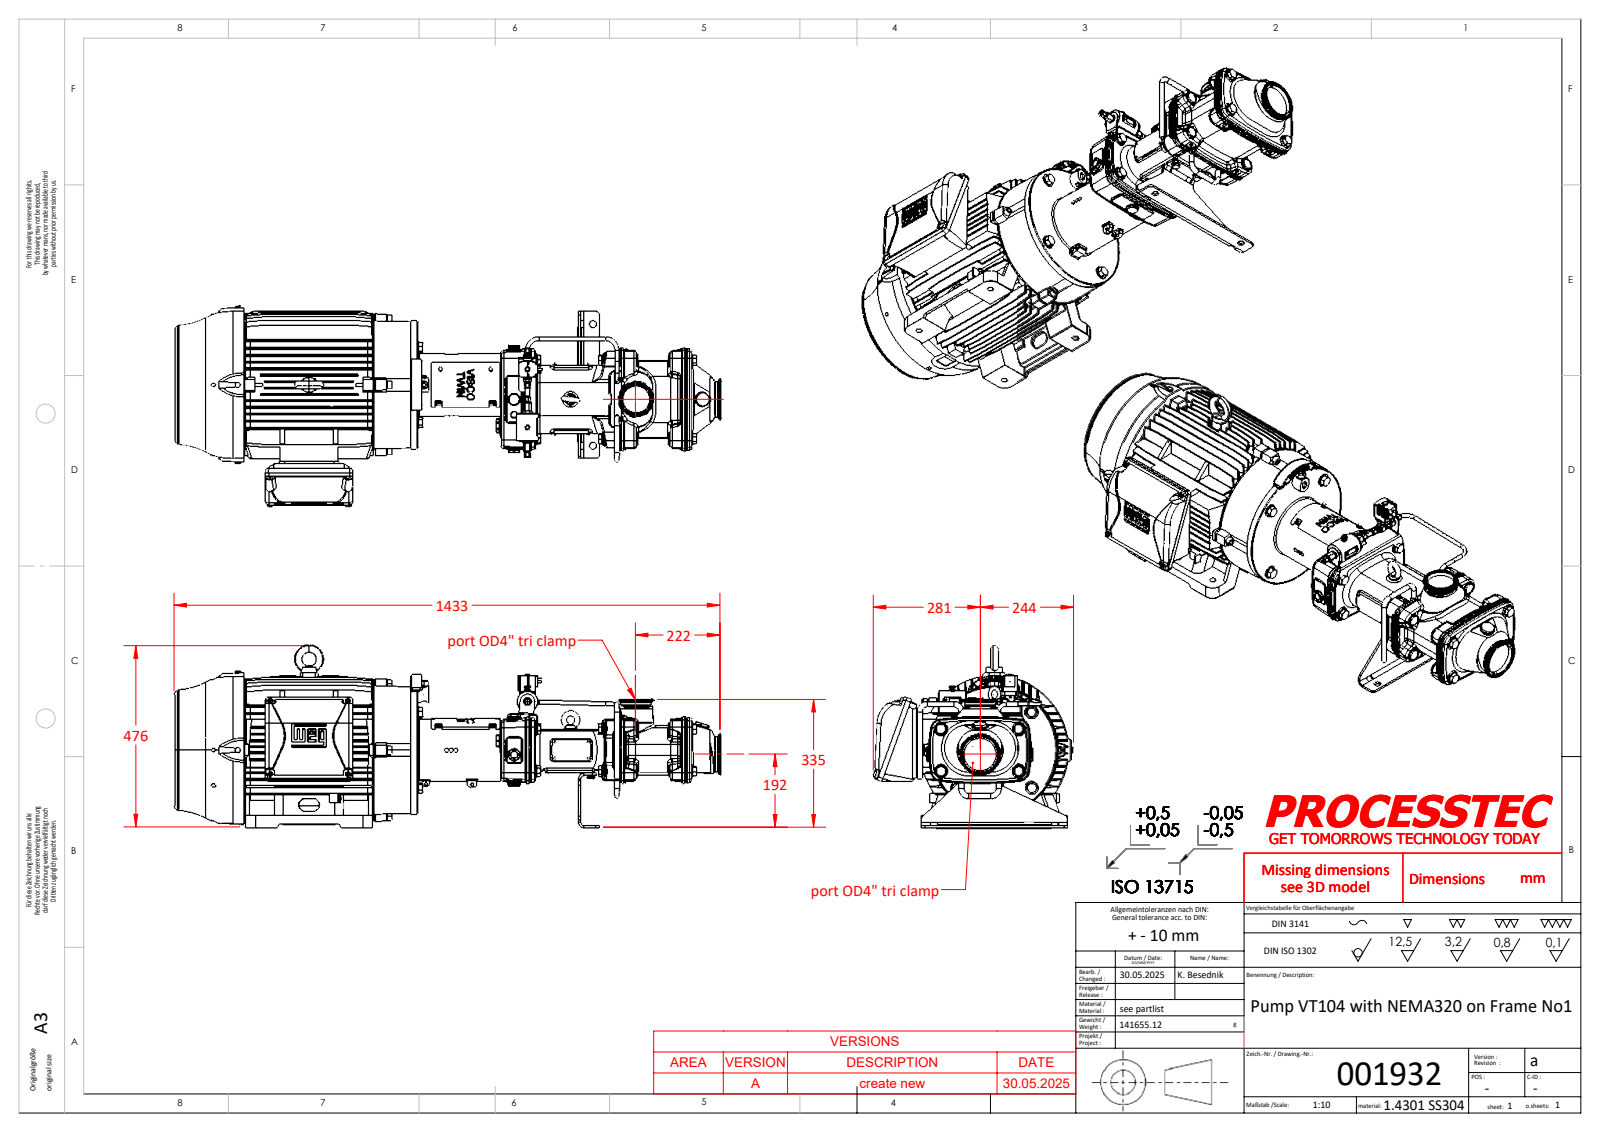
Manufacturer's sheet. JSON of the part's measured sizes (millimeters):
{"part_name": "001402; 001073; 001187_Washer ISO 7089 - 10; 001074 (+8 more)", "step_written_by": "SolidWorks 2023 (AUTOMOTIVE_DESIGN)", "units": "millimeters", "bodies": {"solids": 76, "faces": 7986, "planar": 2792, "cylindrical": 2404, "other": 2790}, "overall_size": [1433.05, 525.98, 476.2], "volume_mm3": 82320000, "surface_area_mm2": 4582000, "round_holes": [[8, 15], [8.5, 8], [4.35, 5], [5, 5], [9, 5], [14, 5], [17.5, 5], [18, 5], [2.5, 4], [15.88, 4], [16.66, 4], [16.76, 4]], "round_bosses_or_shafts": [[10, 9], [8, 9], [24, 8], [11.6, 7], [16, 5], [33.32, 4], [30, 4], [18.5, 4]], "partial_cylinders_radius": [[2.98, 188], [2, 60], [5, 58], [3, 42], [1.5, 39], [8, 34], [6, 24], [4, 21]], "face_to_face_distances": [342.3, 102, 444.3, 747.8, 405.5, 303.5, 175.65, 517.95, 619.95, 923.45], "hole_center_spacings": [55, 193.35, 28.75, 67.98, 94.4, 101.37, 107.22, 107.65]}
